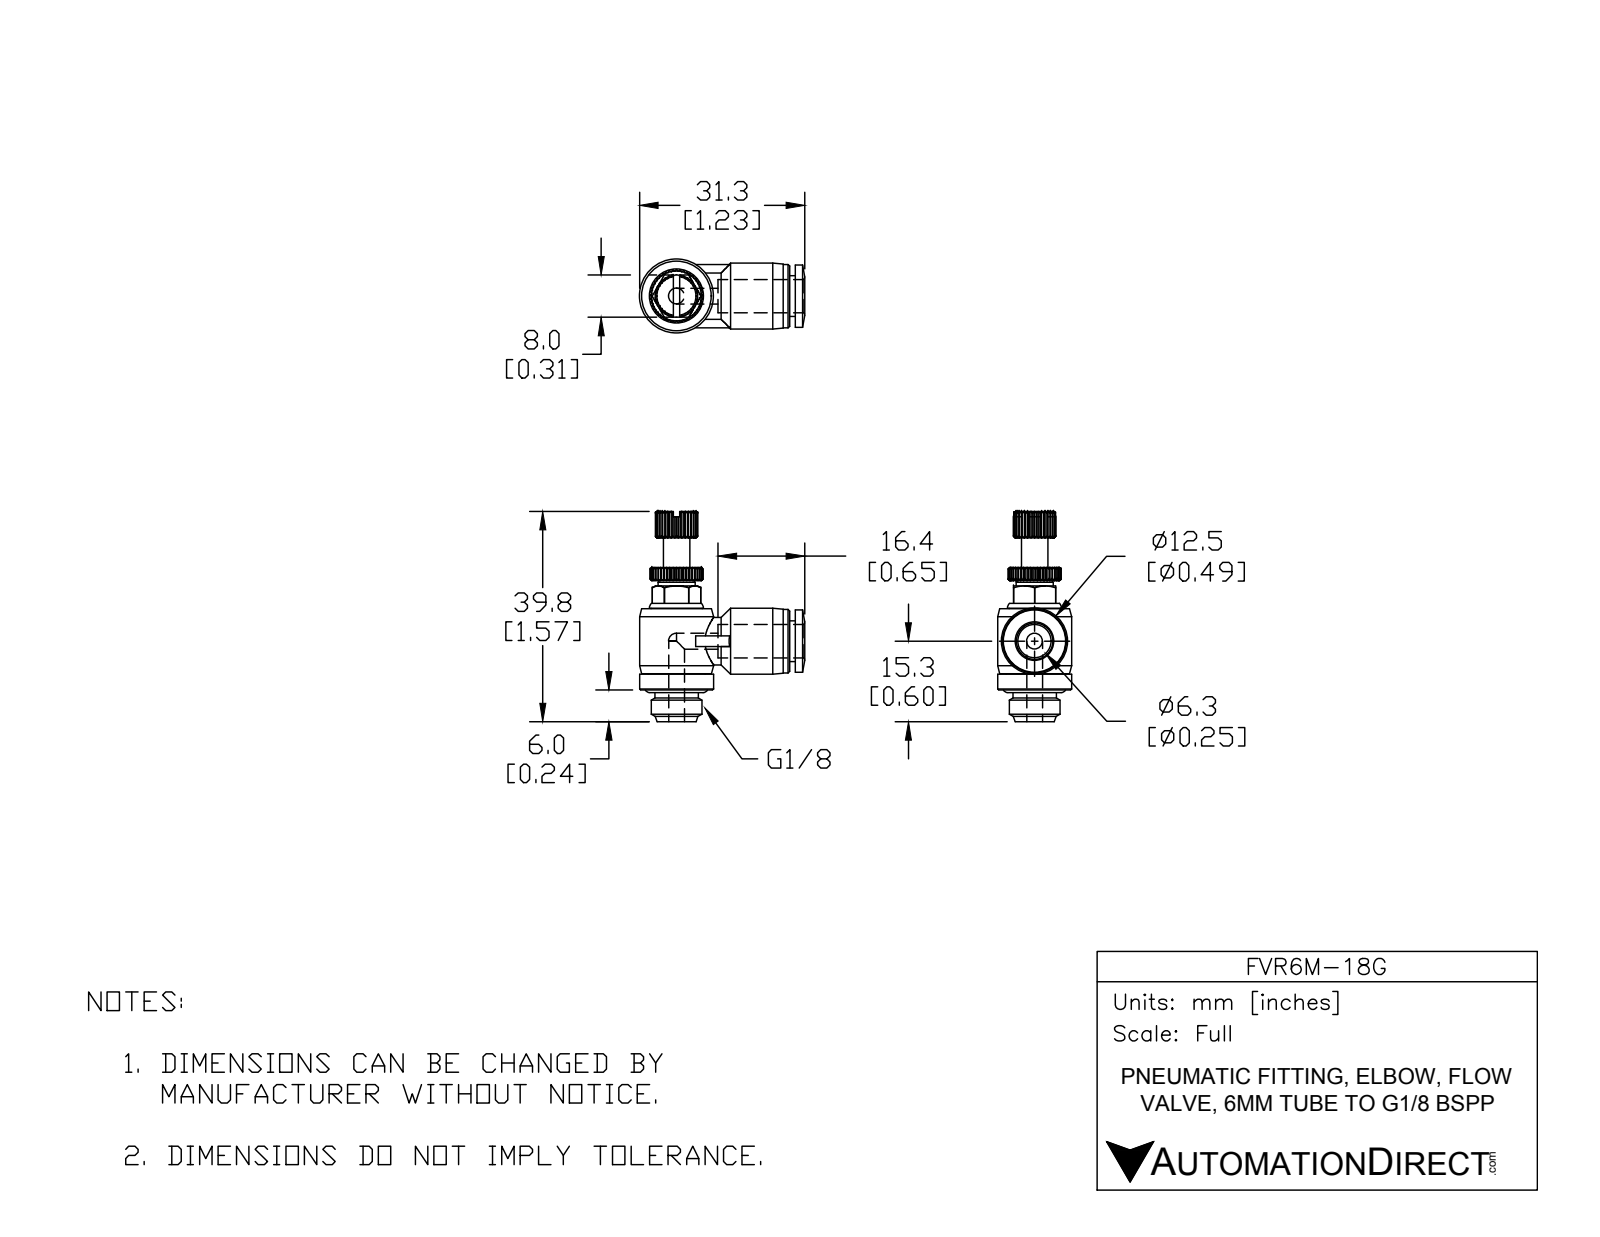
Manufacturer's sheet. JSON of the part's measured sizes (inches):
{"part_name": "FVR6M-18G", "step_written_by": "SolidWorks 2015 (AUTOMOTIVE_DESIGN)", "units": "inches", "bodies": {"solids": 2, "faces": 511, "planar": 192, "cylindrical": 121, "other": 198}, "overall_size": [1.567, 1.23, 0.551], "volume_in3": 0.29, "surface_area_in2": 5.462, "round_holes": [[0.118, 2], [0.248, 1]], "round_bosses_or_shafts": [[0.551, 1], [0.492, 1], [0.472, 1], [0.465, 1], [0.425, 1], [0.382, 1], [0.378, 1], [0.354, 1]], "partial_cylinders_radius": [[0.157, 1], [0.181, 1], [0.197, 1]], "face_to_face_distances": [0.488, 0.041, 0.206, 0.795, 0.307, 0.358, 0.063, 0.551, 0.858, 0.067]}
